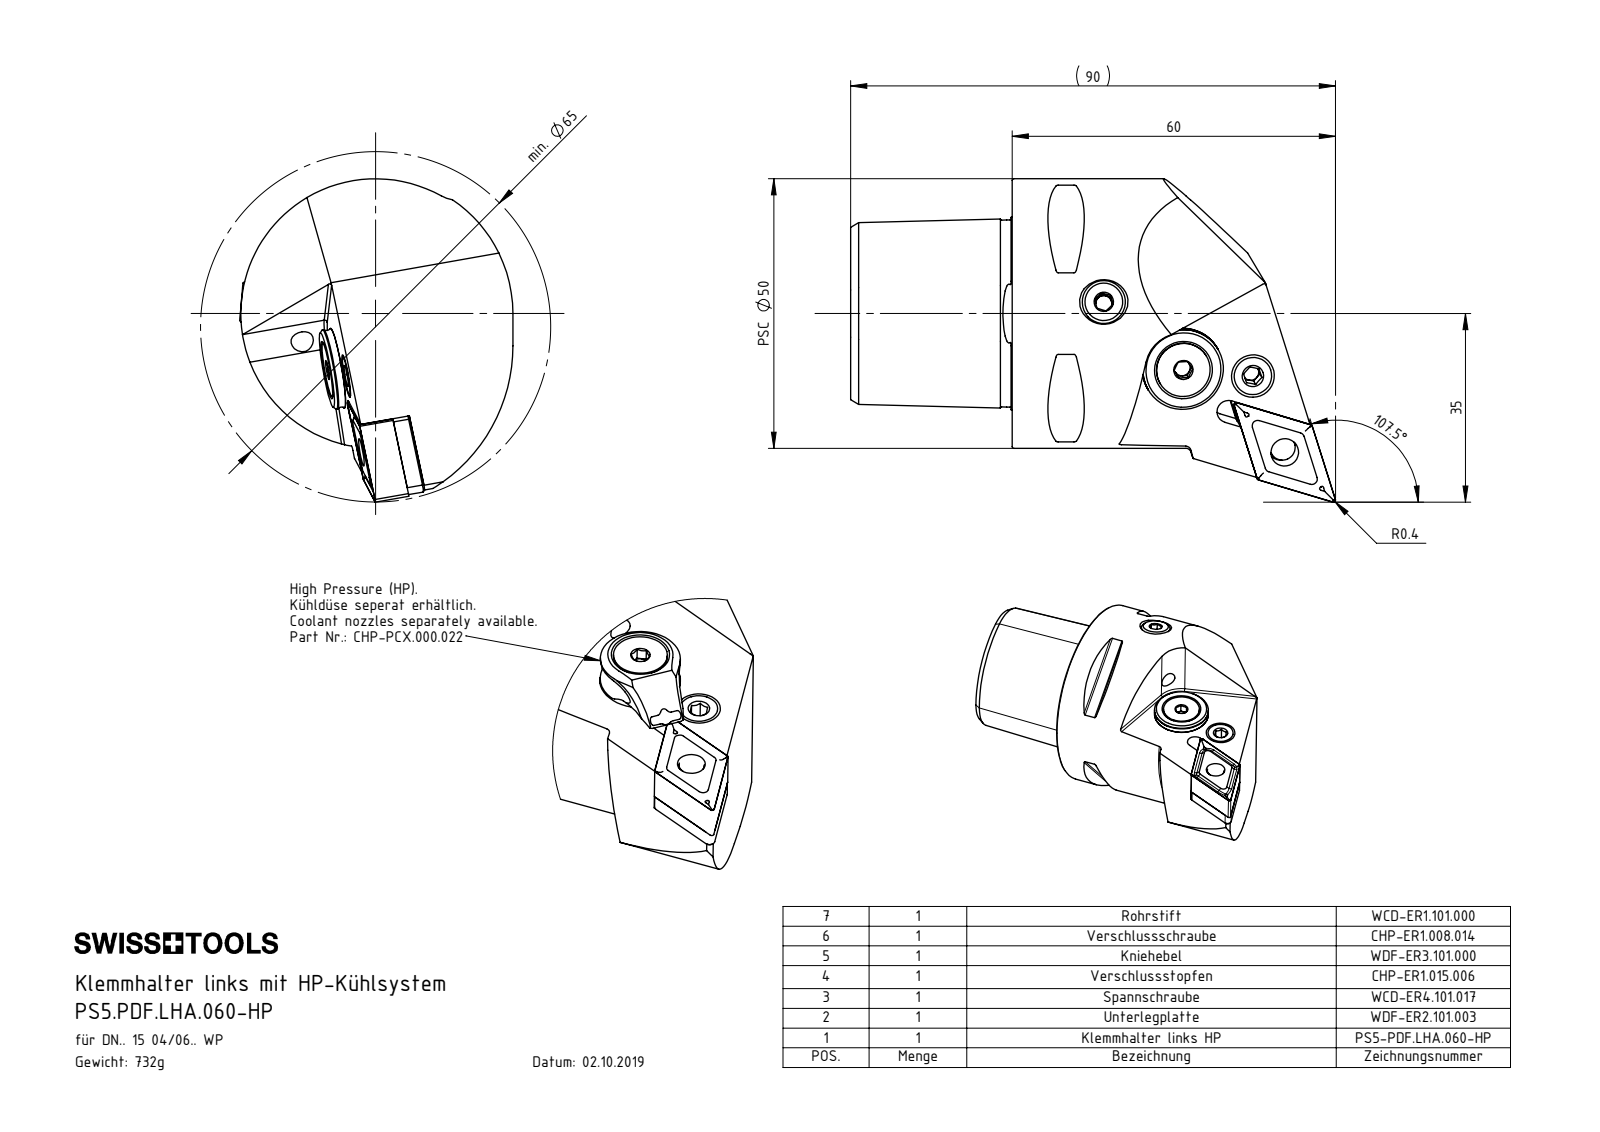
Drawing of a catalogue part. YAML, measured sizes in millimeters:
part_name: "WDF-ER3.101.000_A; WCD-ER4.101.017_A; CHP-ER1.008.014_A; CHP-ER1.015.006_A (+8 more)"
step_written_by: "SolidWorks 2017 (AUTOMOTIVE_DESIGN)"
units: millimeters
bodies: {solids: 11, faces: 441, planar: 129, cylindrical: 113, other: 199}
overall_size: [90.01, 60.01, 50.71]
volume: 94521
surface_area: 24591
round_holes:
  - {diameter: 4.2, count: 3}
  - {diameter: 7, count: 2}
  - {diameter: 1.2, count: 1}
  - {diameter: 2, count: 1}
  - {diameter: 2.5, count: 1}
  - {diameter: 3, count: 1}
  - {diameter: 4, count: 1}
  - {diameter: 5, count: 1}
  - {diameter: 5.16, count: 1}
  - {diameter: 5.2, count: 1}
  - {diameter: 6.1, count: 1}
  - {diameter: 6.4, count: 1}
round_bosses_or_shafts:
  - {diameter: 8, count: 2}
  - {diameter: 50, count: 1}
  - {diameter: 15, count: 1}
  - {diameter: 13.4, count: 1}
  - {diameter: 10, count: 1}
  - {diameter: 7.9, count: 1}
  - {diameter: 6.4, count: 1}
  - {diameter: 5.5, count: 1}
partial_cylinders:
  - {radius: 0.5, count: 10}
  - {radius: 0.4, count: 4}
  - {radius: 1, count: 4}
  - {radius: 2.5, count: 2}
  - {radius: 7, count: 2}
  - {radius: 2.1, count: 1}
  - {radius: 2.35, count: 1}
  - {radius: 2.8, count: 1}
face_to_face_distances: [12.38, 30, 6.04, 0.32, 12.7, 1.54, 4.5, 19.18, 44.4, 3.19]
hole_center_spacings: [4.5, 21.57, 25, 8.8, 13.28, 4.49, 15.6, 15.61]
